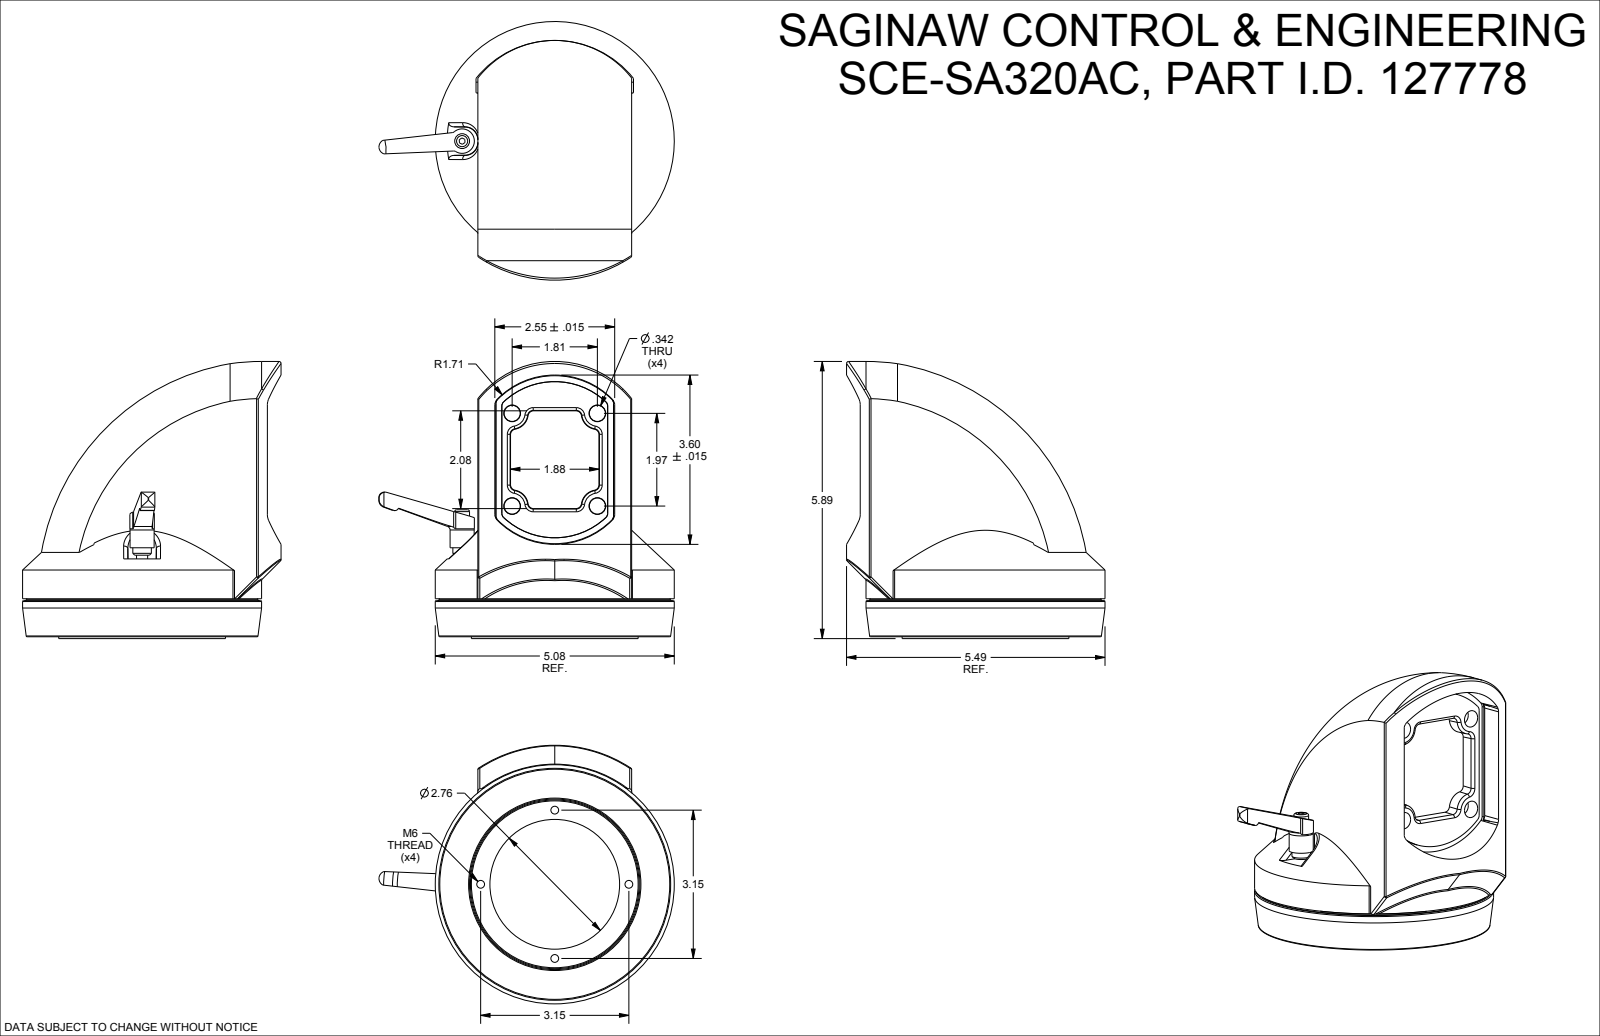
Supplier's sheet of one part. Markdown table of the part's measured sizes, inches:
| quantity | value |
| --- | --- |
| part name | SCE-SA320AC |
| STEP written by | SolidWorks 2023 (AUTOMOTIVE_DESIGN) |
| units | inches |
| bodies | 3 solids, 1263 faces (265 planar, 269 cylindrical, 729 other) |
| overall size | 5.886 × 5.709 × 5.671 |
| volume | 38.37 in³ |
| surface area | 286.7 in² |
| round holes (diameter × count) | 0.197 × 6, 0.374 × 6, 0.335 × 5, 0.165 × 4, 0.217 × 4, 0.394 × 4, 0.441 × 4, 3.418 × 1, 3.622 × 1, 4.173 × 1 |
| round bosses / shafts (diameter × count) | 0.335 × 4, 0.197 × 4, 0.315 × 2, 5.079 × 1, 4.094 × 1, 3.799 × 1, 0.63 × 1, 0.512 × 1 |
| partial cylindrical surfaces (radius × count) | 0.008 × 52, 0.02 × 38, 0.079 × 15, 0.276 × 10, 0.394 × 9, 0.059 × 8, 0.012 × 7, 0.787 × 6 |
| main face-to-face distances | 0.807, 0.709, 0.039, 0.098, 0.315, 1.083, 0.748, 0.984, 1.831, 1.791 |
| hole center spacings | 2.725, 0.987, 0.65, 1.574, 2.224, 2.227, 2.53, 3.146 |
